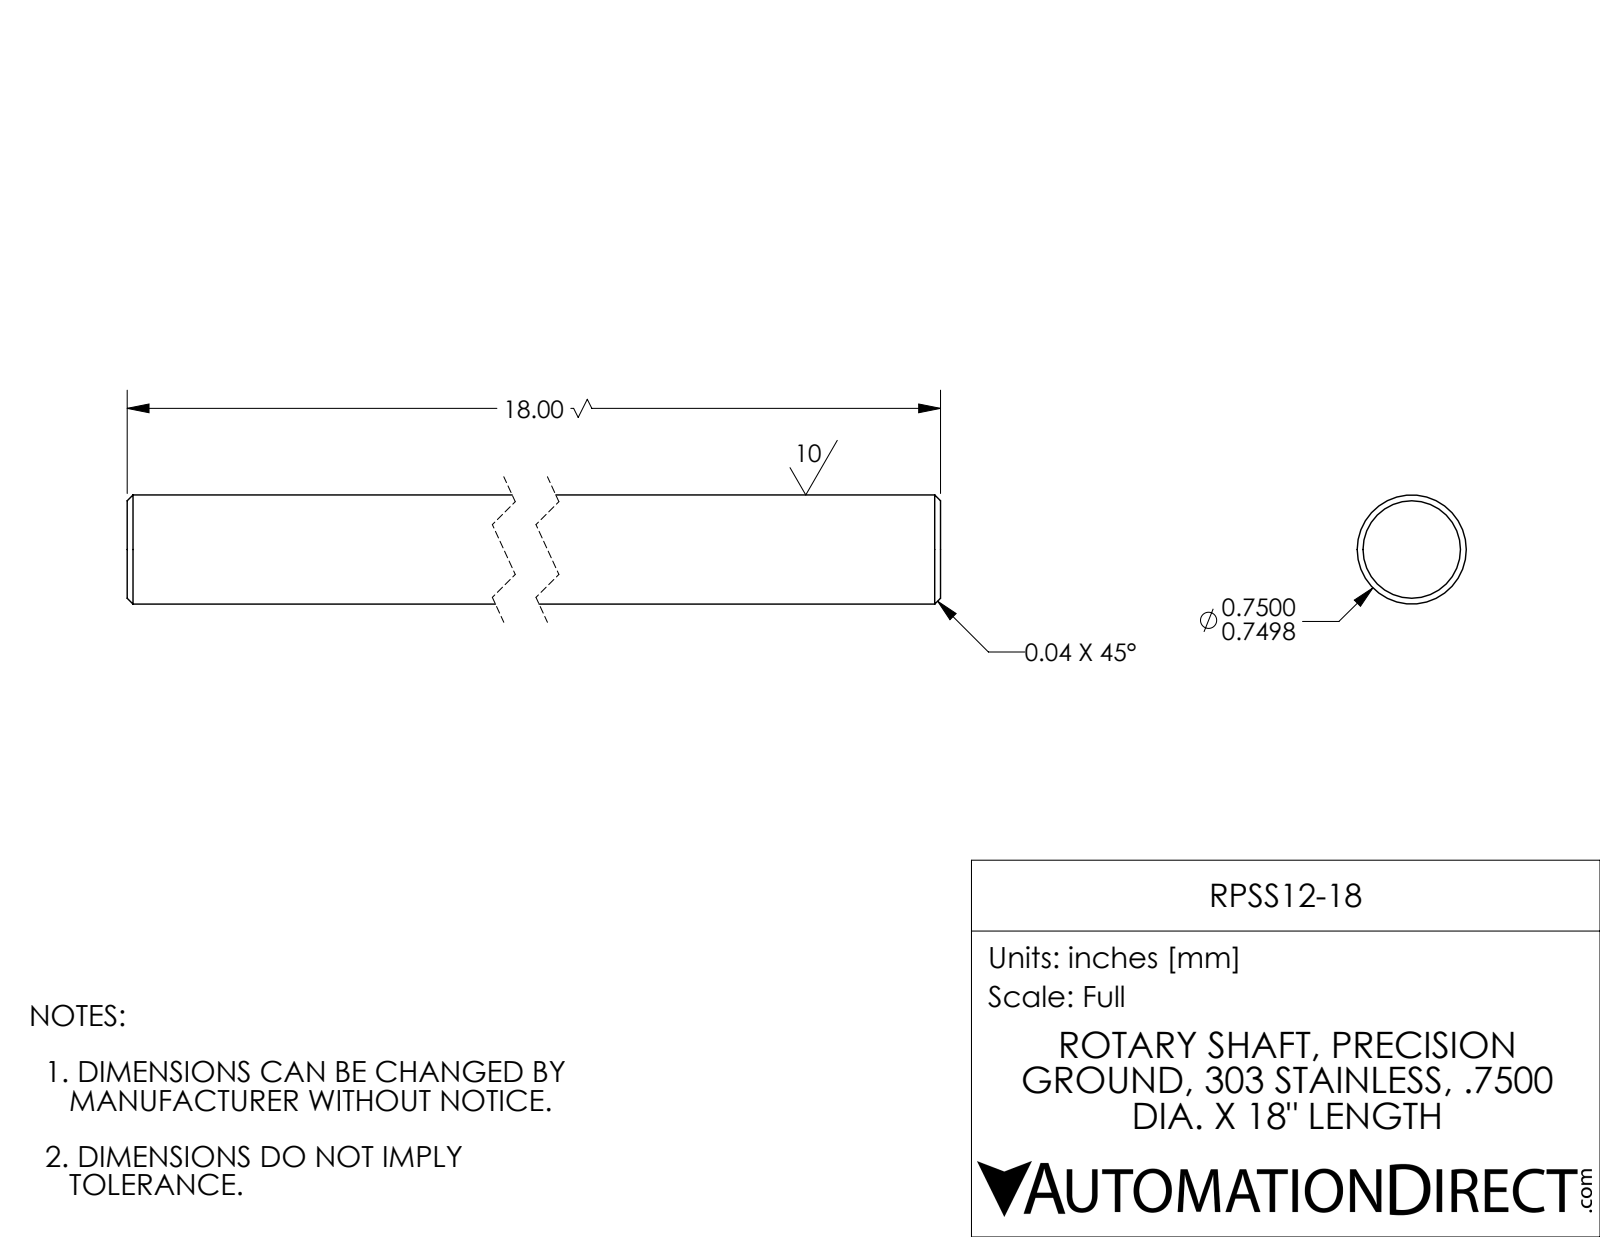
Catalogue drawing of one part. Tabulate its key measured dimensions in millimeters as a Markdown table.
| quantity | value |
| --- | --- |
| part name | RPSS12-18 |
| STEP written by | SolidWorks 2017 (AUTOMOTIVE_DESIGN) |
| units | millimeters |
| bodies | 1 solid, 8 faces (2 planar, 2 cylindrical, 4 other) |
| overall size | 457.2 × 19.1 × 19.1 |
| volume | 130 300 mm³ |
| surface area | 27 860 mm² |
| round bosses / shafts (diameter × count) | 19.1 × 1 |
| main face-to-face distances | 457.2 |
